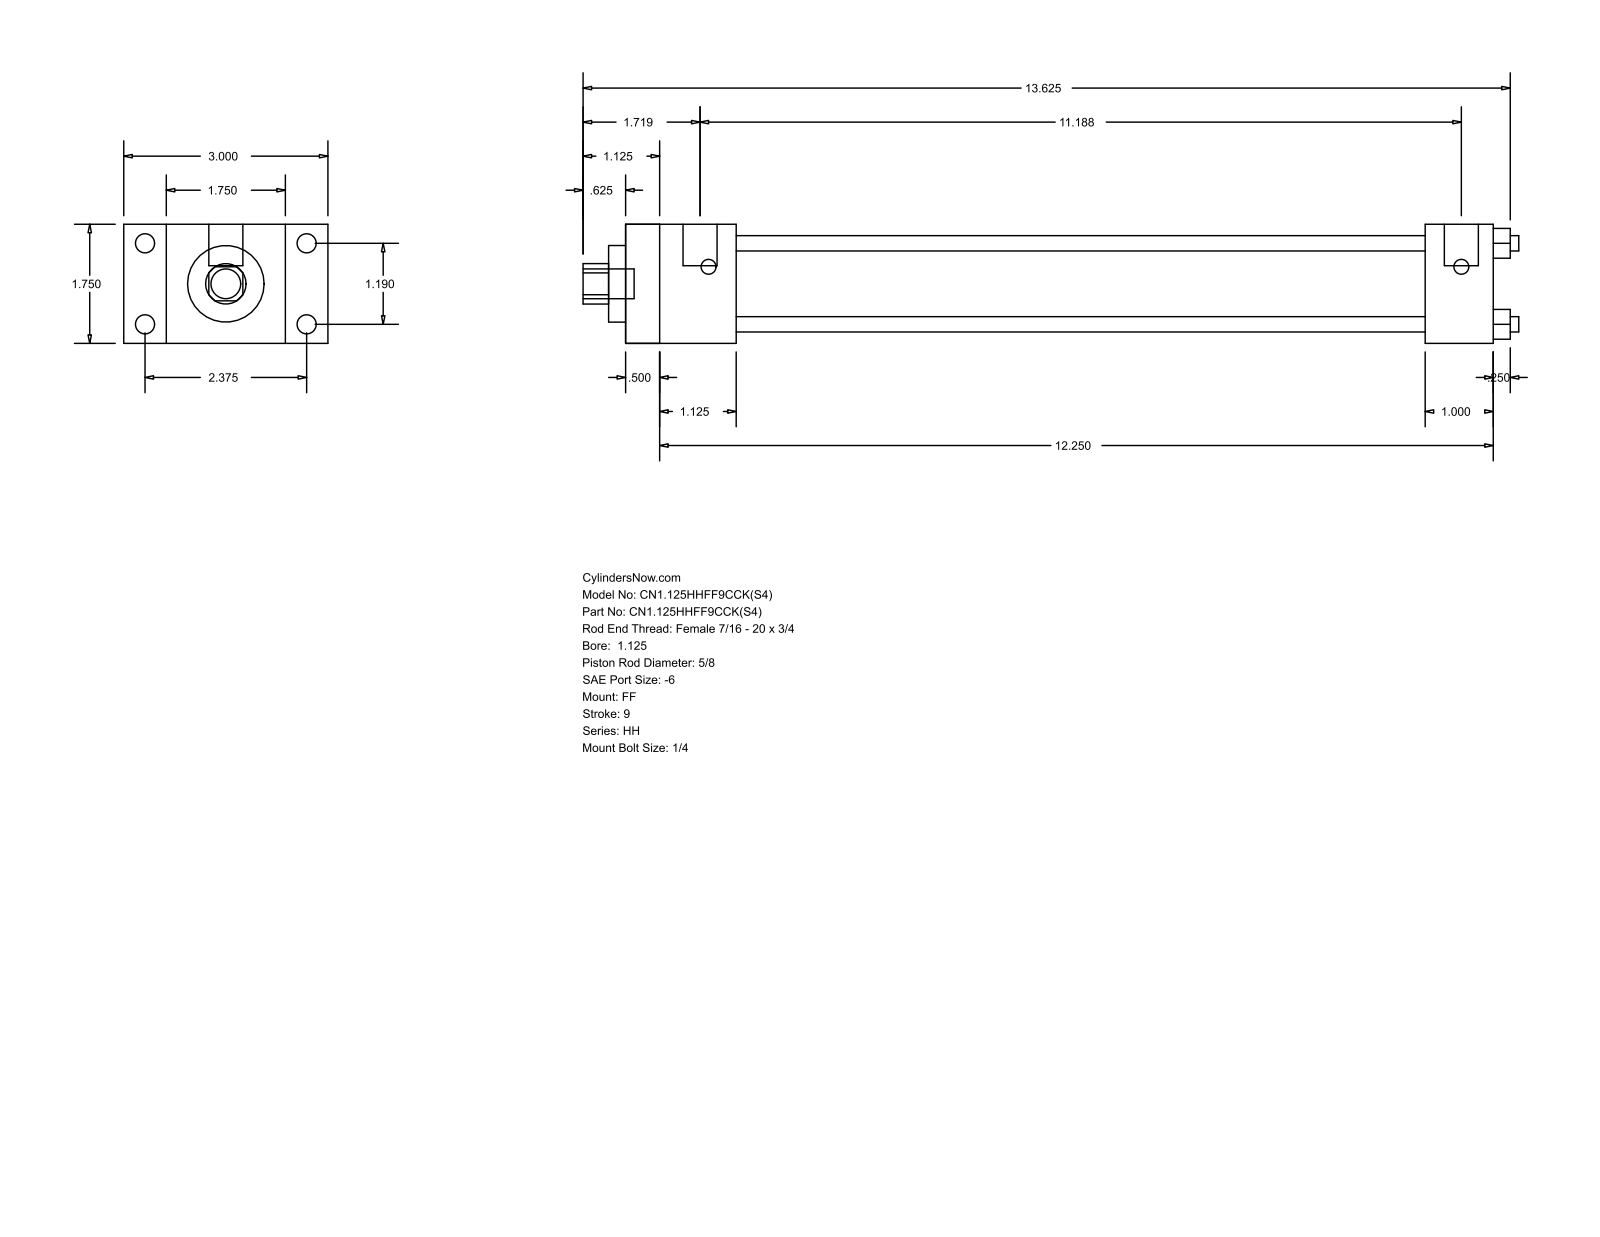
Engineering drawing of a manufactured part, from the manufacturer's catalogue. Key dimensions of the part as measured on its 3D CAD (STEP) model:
Part name (STEP PRODUCT): HH_FF__0112_0.625
STEP written by: GSSL Pune (CONFIG_CONTROL_DESIGN)
Units: millimetres
Bodies: 0 solids, 92 faces (64 planar, 28 cylindrical, 0 other)
Overall size (bounding box): 349.25 × 76.2 × 44.45
Round holes (diameter × count): ⌀5.71 ×4, ⌀15.88 ×1, ⌀28.57 ×1, ⌀34.92 ×1
Round bosses / shafts (diameter × count): ⌀7.14 ×4, ⌀5.56 ×4, ⌀12.7 ×2, ⌀11.11 ×1
Partial cylindrical surfaces — rounded edges, fillets, slot ends (radius × count): R7.54 ×1
Main face-to-face distances: 44.46, 323.85, 12.69, 311.16, 15.87, 60.33, 28.58, 41.27, 298.44, 285.75
Hole centre spacings: 21.37, 30.22, 42.74
